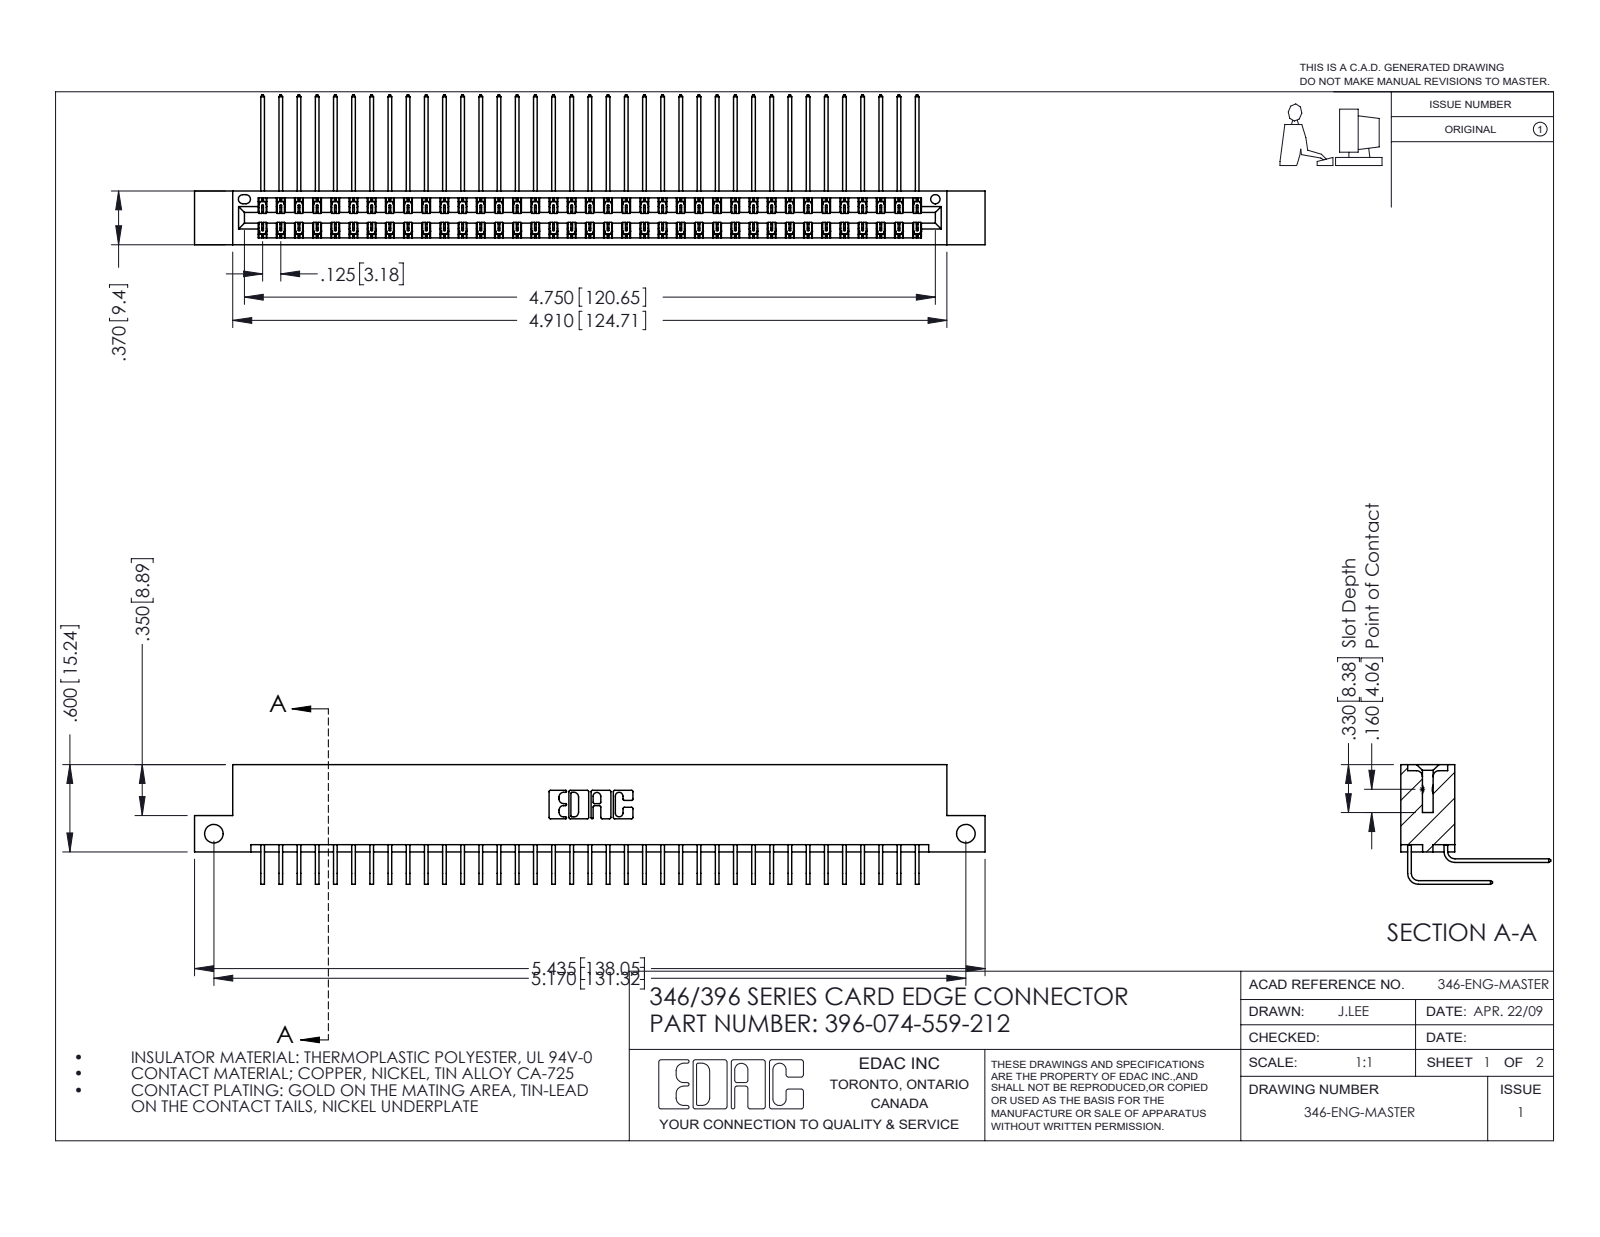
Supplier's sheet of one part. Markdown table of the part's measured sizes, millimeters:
| quantity | value |
| --- | --- |
| part name | 345-292-001_558 559 Tail - 1; 396-074-559-212; 346 Part_Flush Mounting Lugs - Side Mount; 345-292-001_559 Tail - 2 |
| STEP written by | SolidWorks 2016 (CONFIG_CONTROL_DESIGN) |
| units | millimeters |
| bodies | 75 solids, 4118 faces (2814 planar, 1304 cylindrical, 0 other) |
| overall size | 138 × 26.2 × 20.9 |
| volume | 13 800 mm³ |
| surface area | 20 750 mm² |
| round holes (diameter × count) | 3.3 × 2, 1.6 × 1 |
| partial cylindrical surfaces (radius × count) | 0.2 × 111, 0.3 × 22, 0.2 × 6, 0.8 × 6, 0.7 × 3, 0.4 × 2, 0.6 × 2, 0.6 × 2 |
| main face-to-face distances | 1.2, 8.2, 0.6, 6.4, 9.4, 1.8, 7.6, 7, 3.8, 5.6 |
| hole center spacings | 131.3 |
